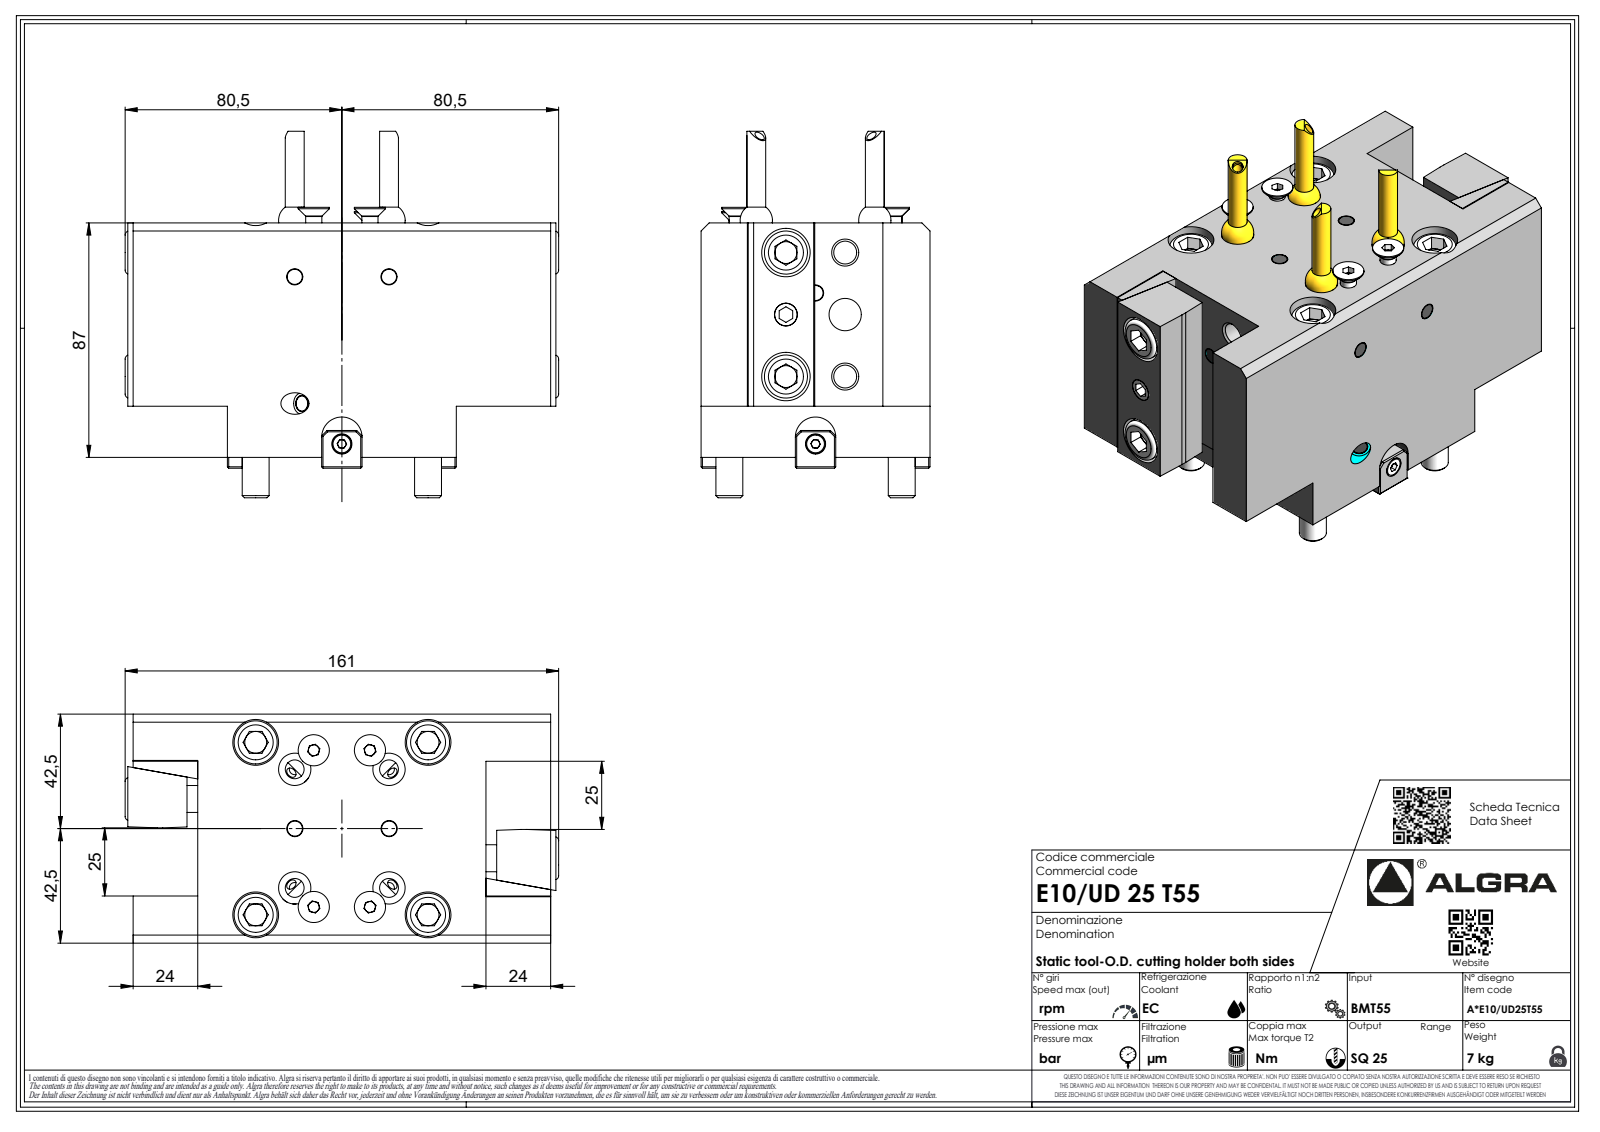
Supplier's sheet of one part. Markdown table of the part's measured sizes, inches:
| quantity | value |
| --- | --- |
| part name | E10UD25T55 |
| STEP written by | SolidWorks 2023 (AUTOMOTIVE_DESIGN) |
| units | inches |
| bodies | 1 solid, 390 faces (266 planar, 46 cylindrical, 78 other) |
| overall size | 6.258 × 5.354 × 3.346 |
| volume | 58.99 in³ |
| surface area | 116.8 in² |
| round holes (diameter × count) | 0.157 × 4, 0.083 × 1 |
| round bosses / shafts (diameter × count) | 0.394 × 4, 0.276 × 4, 0.251 × 1, 0.067 × 1 |
| partial cylindrical surfaces (radius × count) | 0.013 × 7, 0.02 × 7, 0.146 × 7, 0.079 × 4, 0.008 × 1 |
| main face-to-face distances | 3.346, 3.425, 0.748, 2.677, 0.433, 0.945, 5.157, 1.378, 0.689, 4.724 |
